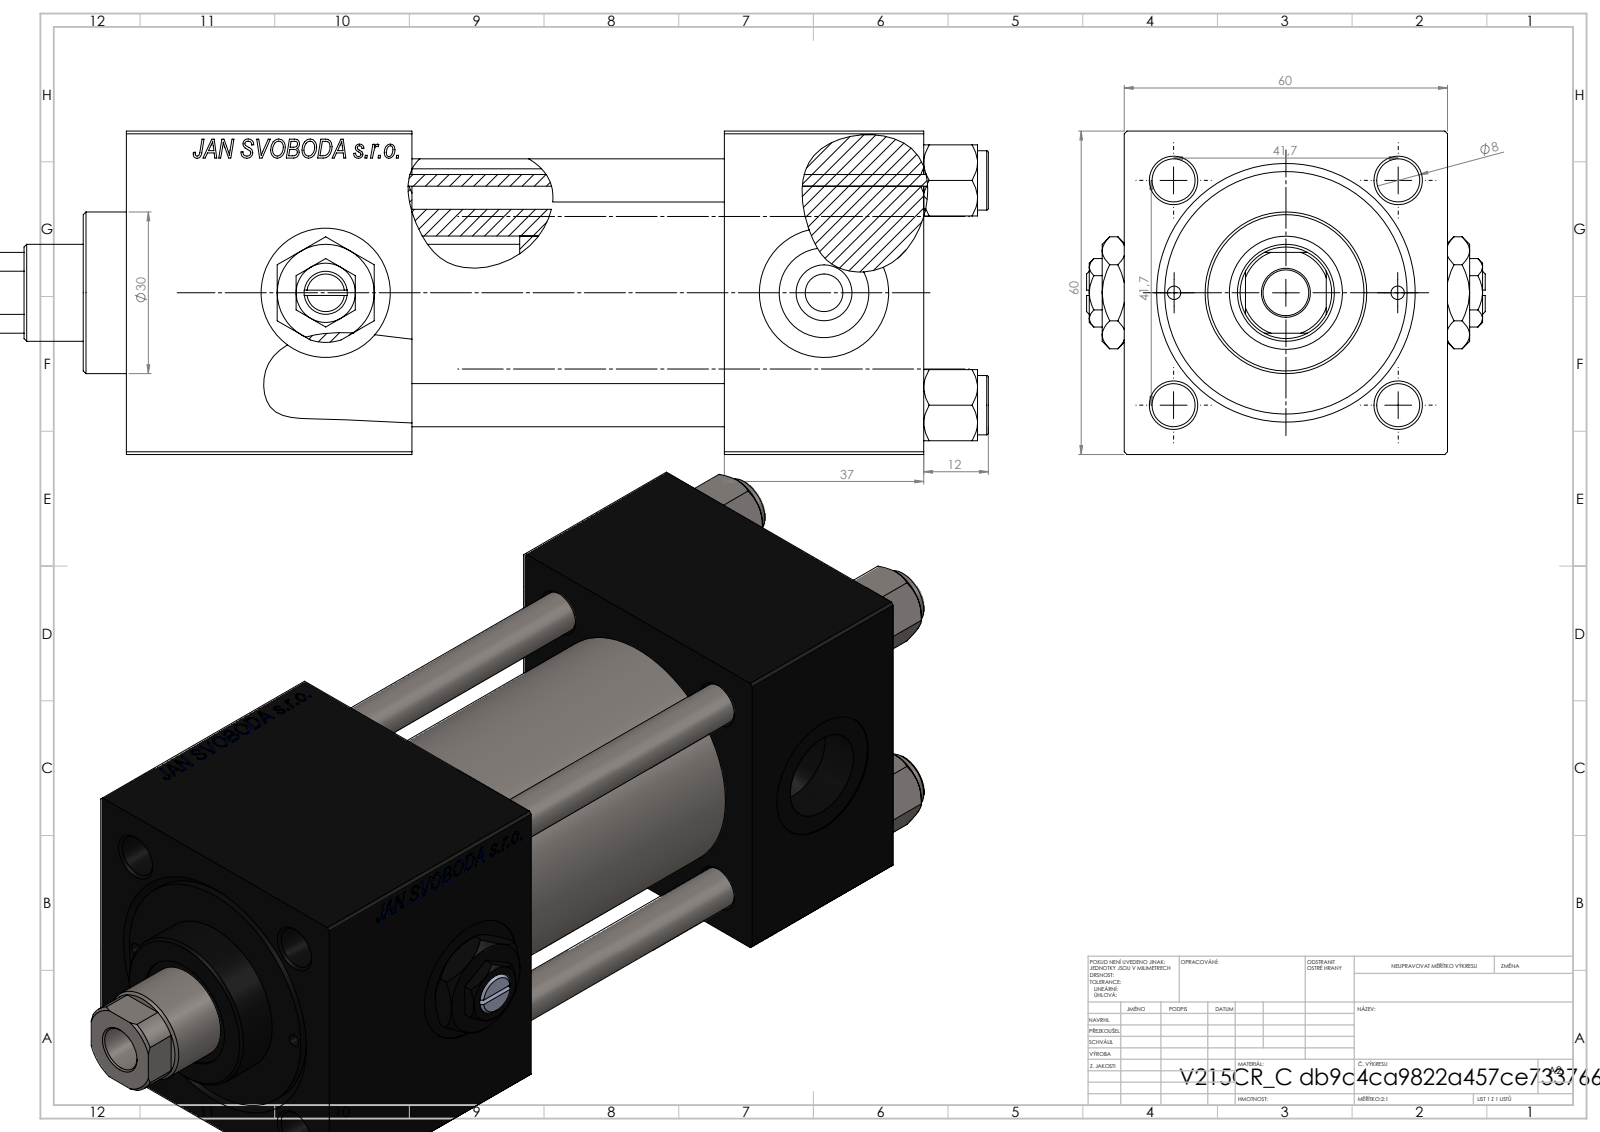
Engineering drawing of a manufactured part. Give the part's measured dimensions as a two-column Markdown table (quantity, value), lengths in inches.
| quantity | value |
| --- | --- |
| part name | V215CR_C_TYCINKA; V215_VC_A; V215CR_C_Body; NUT_M5_C (+2 more) |
| STEP written by | SolidWorks 2019 (CONFIG_CONTROL_DESIGN) |
| units | inches |
| bodies | 13 solids, 1256 faces (576 planar, 102 cylindrical, 578 other) |
| overall size | 7.283 × 2.913 × 2.362 |
| volume | 24.37 in³ |
| surface area | 167.9 in² |
| round holes (diameter × count) | 0.315 × 4, 0.098 × 2, 0.276 × 2, 0.656 × 2, 0.945 × 2, 0.335 × 1, 0.709 × 1, 0.827 × 1, 1.22 × 1, 1.575 × 1, 1.772 × 1 |
| round bosses / shafts (diameter × count) | 0.433 × 4, 1.811 × 1, 1.181 × 1 |
| partial cylindrical surfaces (radius × count) | 0.335 × 1 |
| main face-to-face distances | 2.362, 1.457, 2.087, 5.827, 4.37, 2.283, 3.74, 4.697, 3.24, 0.957 |
| hole center spacings | 0.821, 1.161, 1.642, 1.832, 0.817, 2.322, 1.634, 3.642 |
